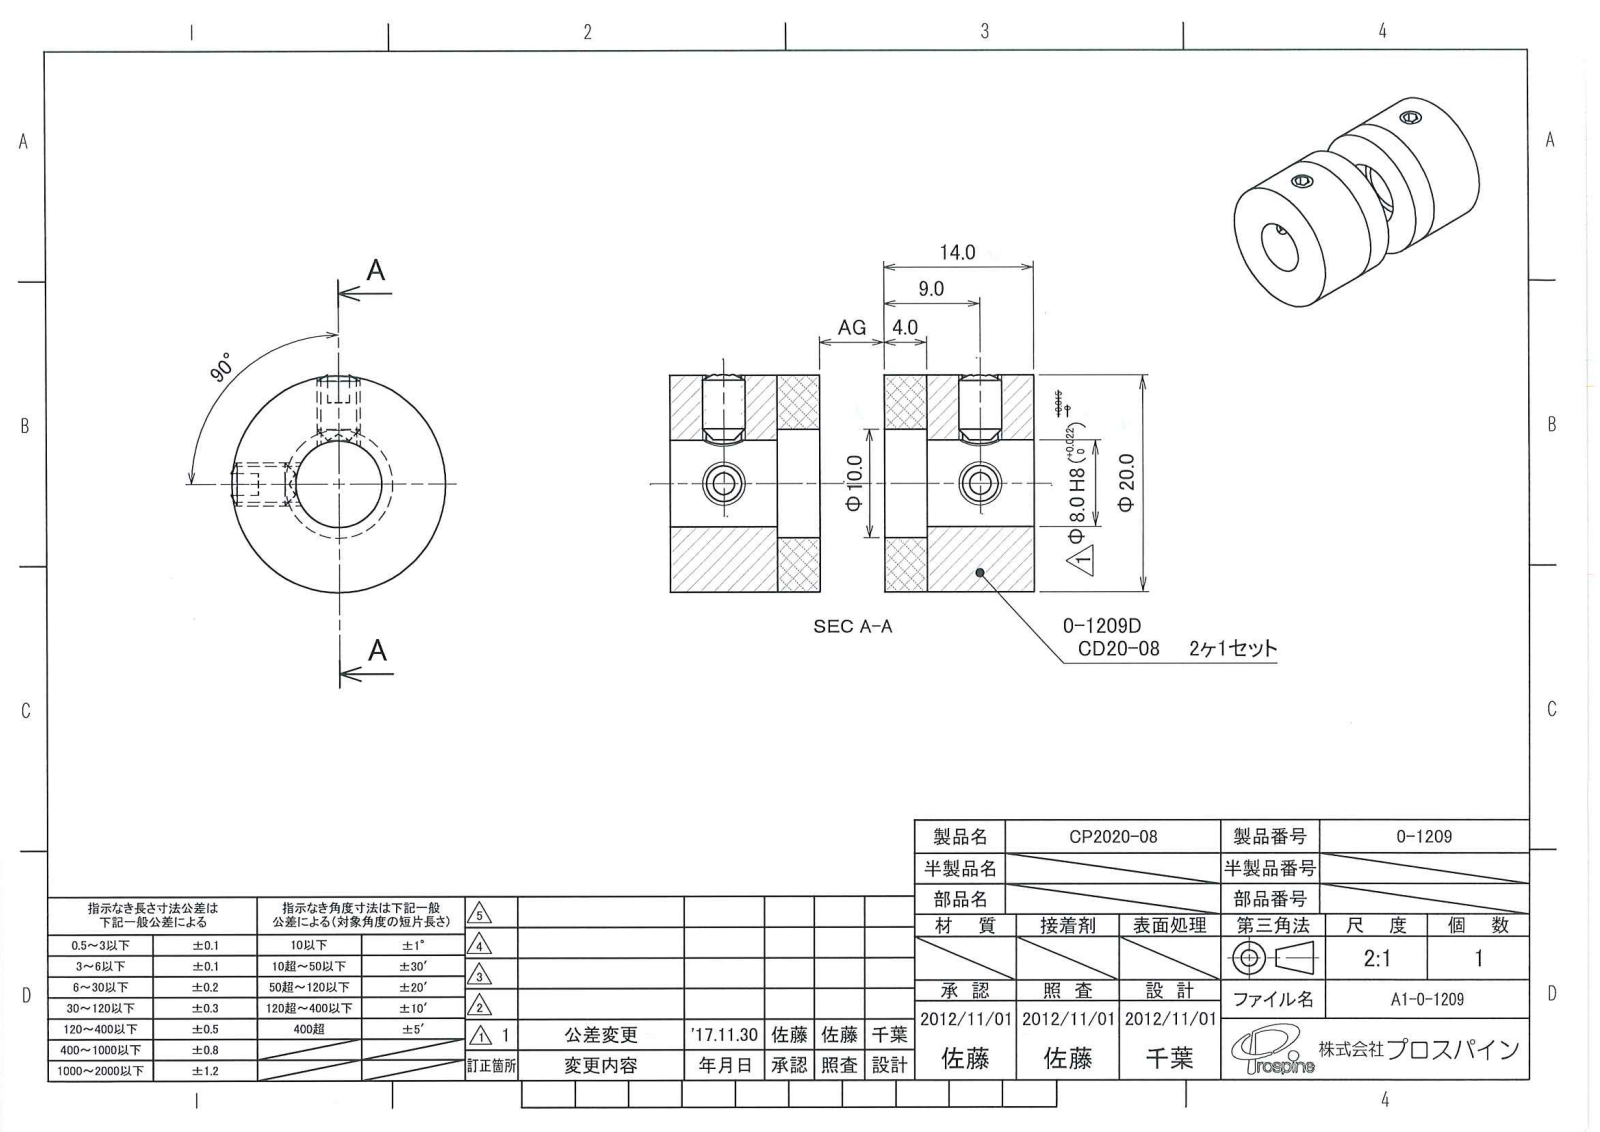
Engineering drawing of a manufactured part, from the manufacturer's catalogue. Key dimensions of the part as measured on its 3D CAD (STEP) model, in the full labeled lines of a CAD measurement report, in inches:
STEP written by: PSStep 10.0 (CONFIG_CONTROL_DESIGN)
Units: inches
Bodies: 5 solids, 43 faces (25 planar, 9 cylindrical, 9 other)
Overall size (bounding box): 0.787 × 0.787 × 0.63
Volume: 0.223 in³ · Surface area: 4.123 in²
Round holes (diameter × count): ⌀0.13 ×2, ⌀0.315 ×1, ⌀0.394 ×1
Round bosses / shafts (diameter × count): ⌀0.157 ×3, ⌀0.787 ×1
Main face-to-face distances: 0.394, 0.551, 0.157, 0.079, 0.256, 0.335, 0.531, 0.138, 0.02
